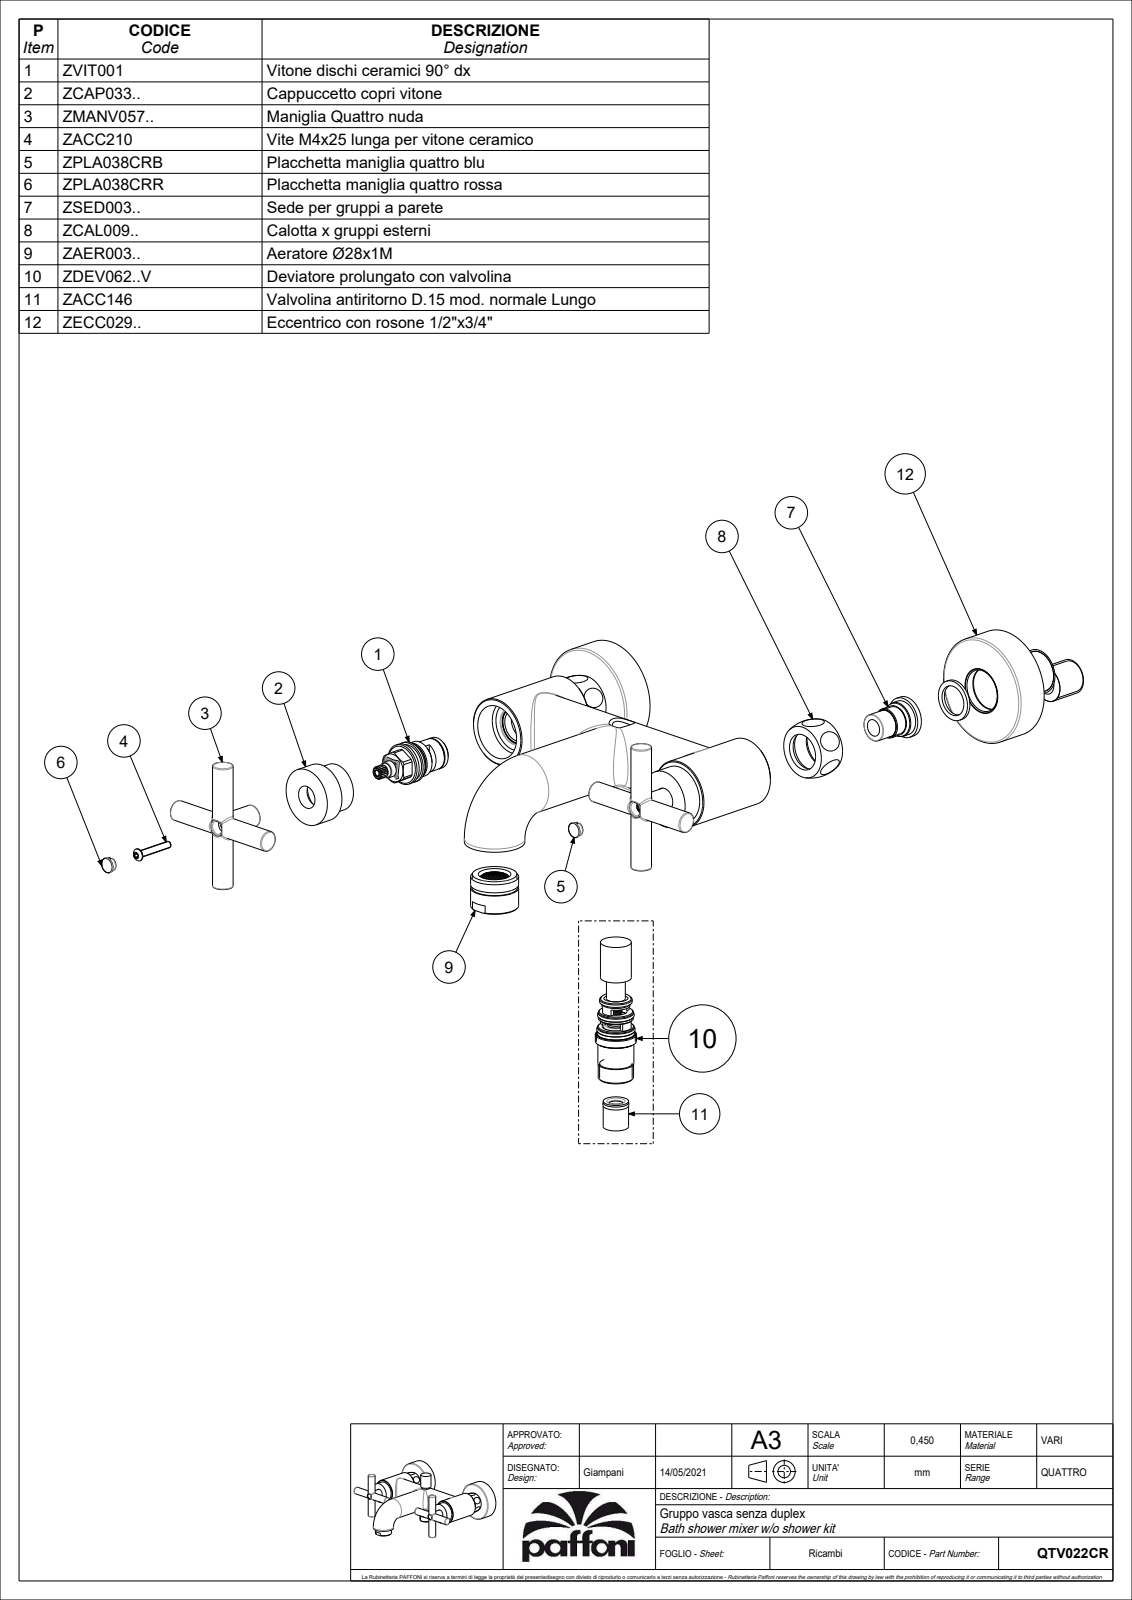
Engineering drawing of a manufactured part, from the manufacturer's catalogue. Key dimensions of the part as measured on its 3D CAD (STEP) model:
Part name (STEP PRODUCT): QTV022CR
STEP written by: CREO PARAMETRIC BY PTC INC, 2020044 (CONFIG_CONTROL_DESIGN)
Units: millimetres
Bodies: 4 solids, 2614 faces (1960 planar, 345 cylindrical, 309 other)
Overall size (bounding box): 225 × 189.05 × 84.61
Volume: 289 376 mm³ · Surface area: 154 045 mm²
Round holes (diameter × count): ⌀10 ×3, ⌀18 ×3, ⌀25 ×3, ⌀3.3 ×2, ⌀4.5 ×2, ⌀7 ×2, ⌀8 ×2, ⌀8.8 ×2, ⌀9.5 ×2, ⌀13.5 ×2, ⌀16.3 ×2, ⌀16.5 ×2
Round bosses / shafts (diameter × count): ⌀24 ×3, ⌀20.5 ×3, ⌀12 ×3, ⌀63.5 ×2, ⌀40 ×2, ⌀35.3 ×2, ⌀34 ×2, ⌀27 ×2
Partial cylindrical surfaces — rounded edges, fillets, slot ends (radius × count): R0.1 ×34, R0.5 ×4, R1 ×4, R3 ×2, R9.4 ×2, R2 ×1, R5.35 ×1, R9.75 ×1
Main face-to-face distances: 0.6, 67.8, 56.8, 12, 11, 18.5, 19.1, 1, 86.9, 86.3
Hole centre spacings: 75, 105, 150
